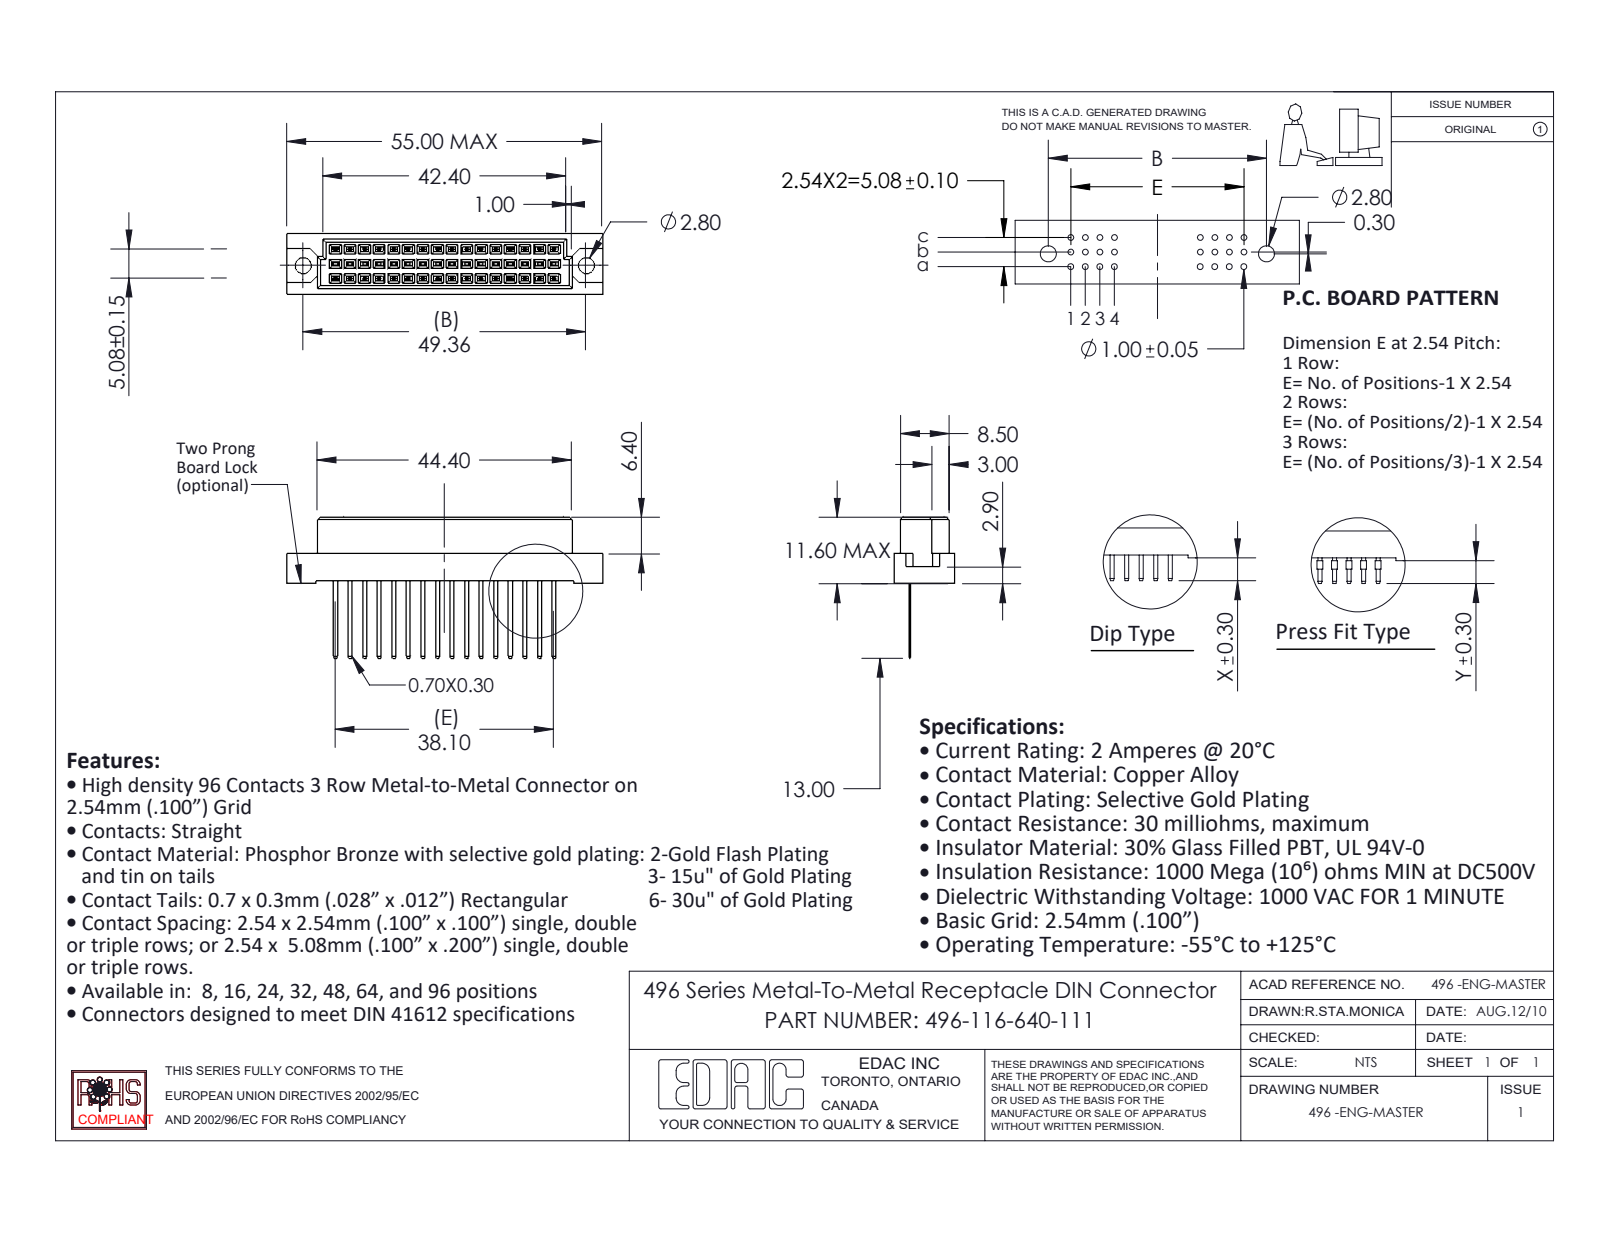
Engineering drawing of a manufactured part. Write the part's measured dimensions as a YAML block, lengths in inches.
part_name: "496 Part_48; 496-116-640-111; 496-290_40"
step_written_by: "SolidWorks 2020 (CONFIG_CONTROL_DESIGN)"
units: inches
bodies: {solids: 17, faces: 826, planar: 822, cylindrical: 4, other: 0}
overall_size: [2.165, 0.969, 0.417]
volume: 0.284
surface_area: 7.401
round_holes:
  - {diameter: 0.11, count: 2}
face_to_face_distances: [0.1, 0.2, 0.041, 0.376, 0.032, 0.103, 0.115, 0.303, 0.315, 0.061]
hole_center_spacings: [1.943]
